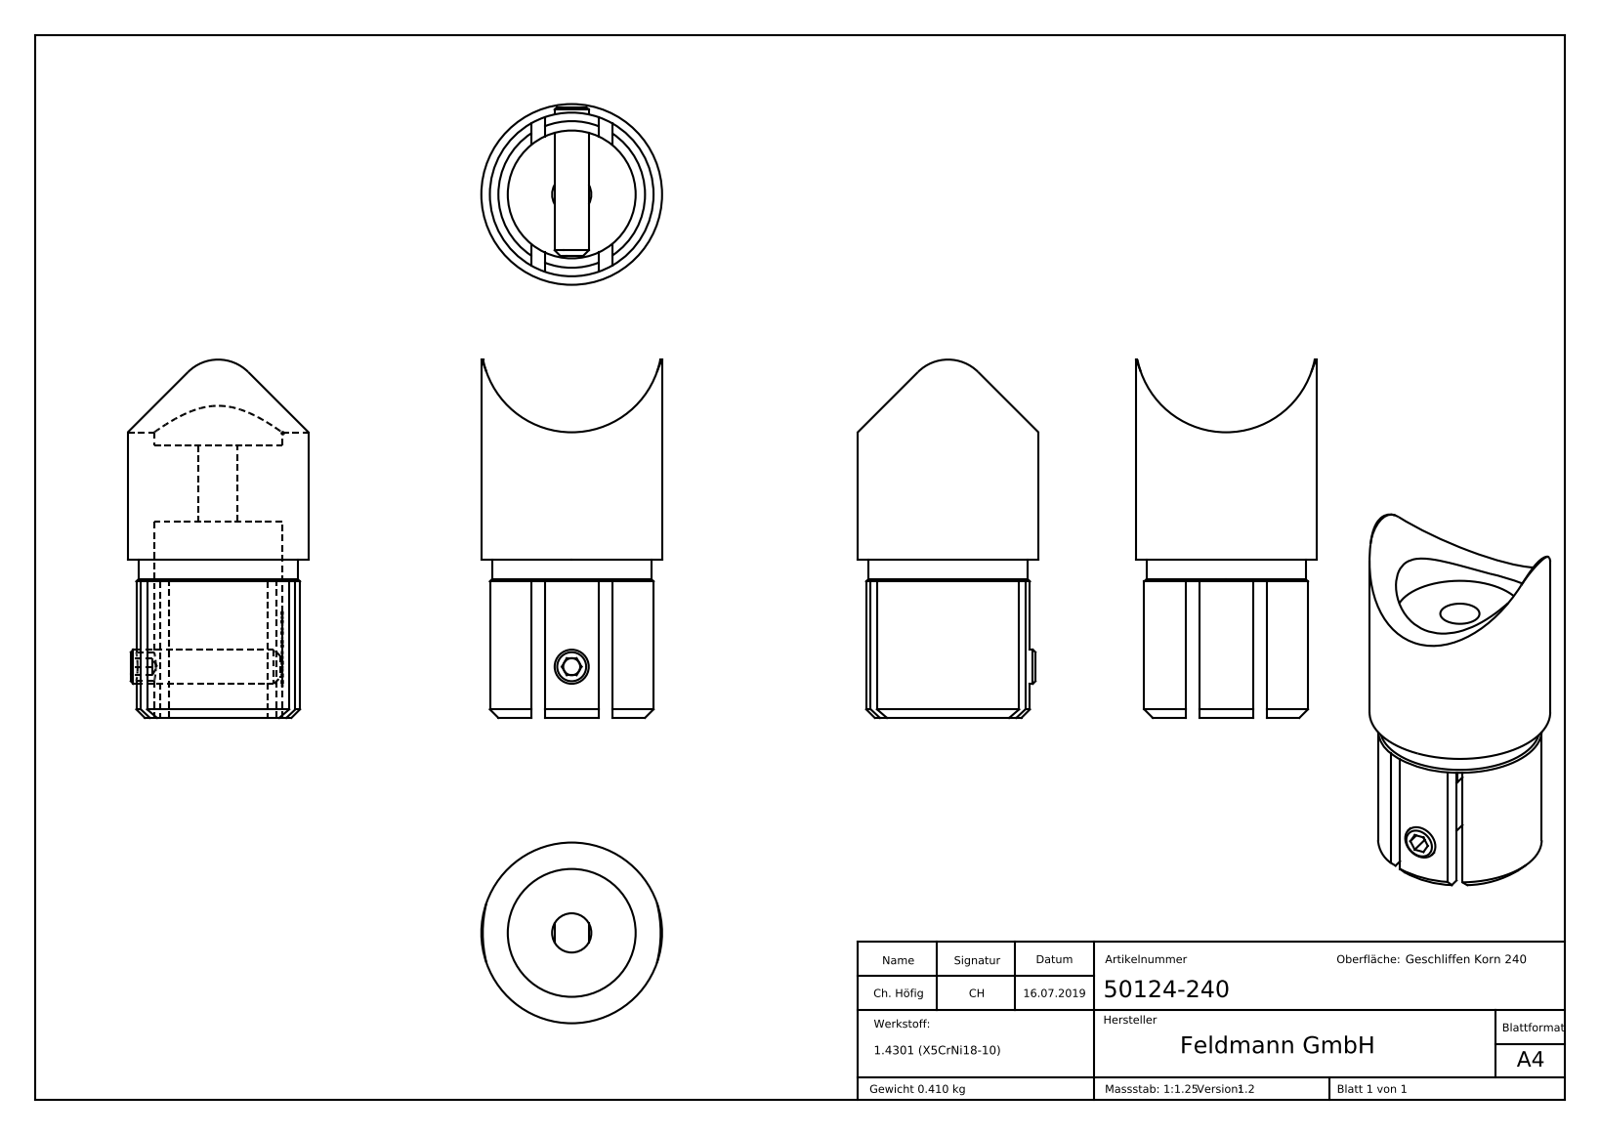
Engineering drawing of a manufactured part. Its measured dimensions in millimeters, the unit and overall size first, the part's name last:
Units: millimetres
Overall size (bounding box): 84.06 × 42.4 × 42.4
Round holes (diameter × count): ⌀6.8 ×1, ⌀9.2 ×1, ⌀30 ×1
Round bosses / shafts (diameter × count): ⌀42.4 ×1, ⌀38.4 ×1, ⌀37.4 ×1, ⌀8 ×1
Partial cylindrical surfaces — rounded edges, fillets, slot ends (radius × count): R10 ×1, R15.1 ×1, R21.2 ×1
Main face-to-face distances: 18, 15.8, 3.2, 27, 19, 9, 12.6, 37, 46, 64
Volume: 51 954 mm³ · Surface area: 19 107 mm²
Bodies: 2 solids, 298 faces (141 planar, 58 cylindrical, 99 other)
Part name (STEP PRODUCT): 50124-240; DIN913_DIN 913 M8x35; 5012X-240 Teil1_50124-240 Teil1
STEP written by: SolidWorks 2015 (CONFIG_CONTROL_DESIGN)
